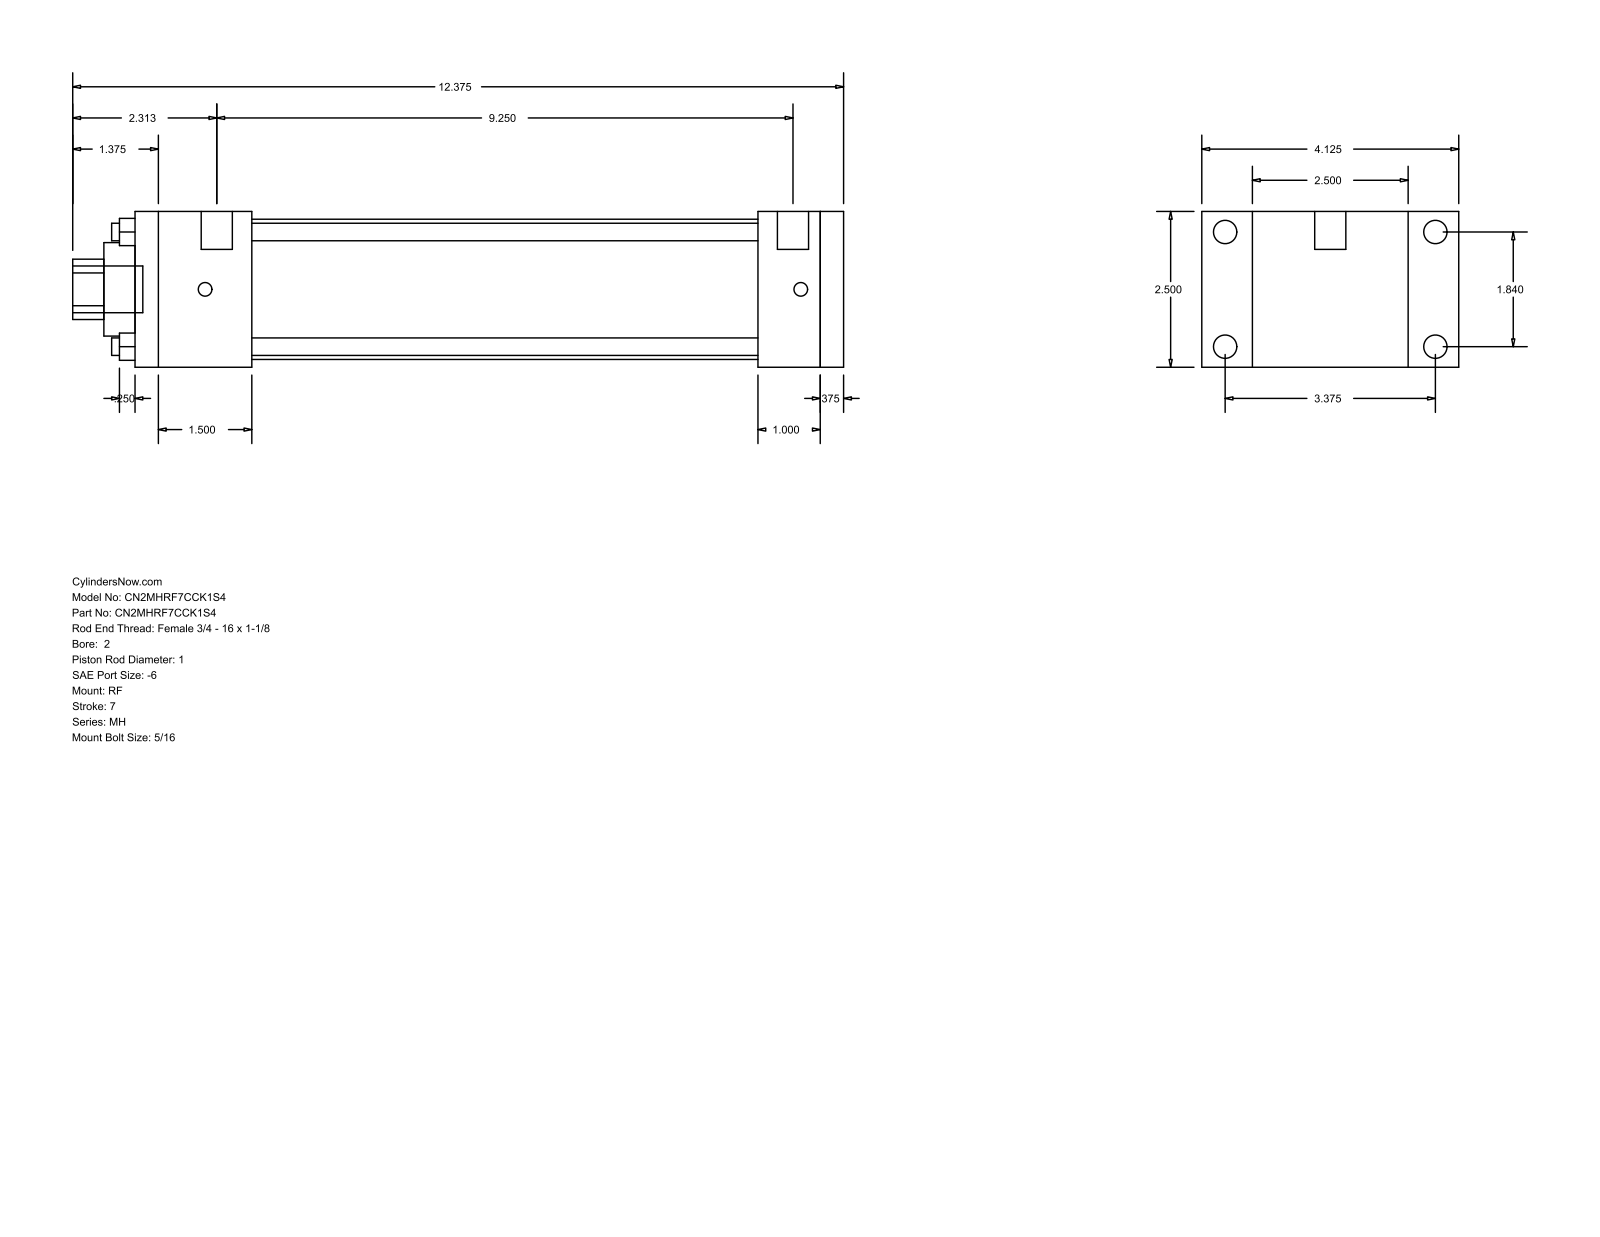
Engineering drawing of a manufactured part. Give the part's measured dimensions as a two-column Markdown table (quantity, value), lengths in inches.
| quantity | value |
| --- | --- |
| part name | MH_RF__0200_1 |
| STEP written by | GSSL Pune (CONFIG_CONTROL_DESIGN) |
| units | inches |
| bodies | 0 solids, 92 faces (64 planar, 28 cylindrical, 0 other) |
| overall size | 12.375 × 4.125 × 2.5 |
| round holes (diameter × count) | 0.281 × 4, 1 × 1, 1.5 × 1, 2.25 × 1 |
| round bosses / shafts (diameter × count) | 0.375 × 4, 0.219 × 4, 0.5 × 2, 0.75 × 1 |
| partial cylindrical surfaces (radius × count) | 0.484 × 1 |
| main face-to-face distances | 2.5, 0.375, 11.375, 11, 0.813, 1, 1.875, 10, 8.125, 9.125 |
| hole center spacings | 1.301, 1.84, 2.602 |
